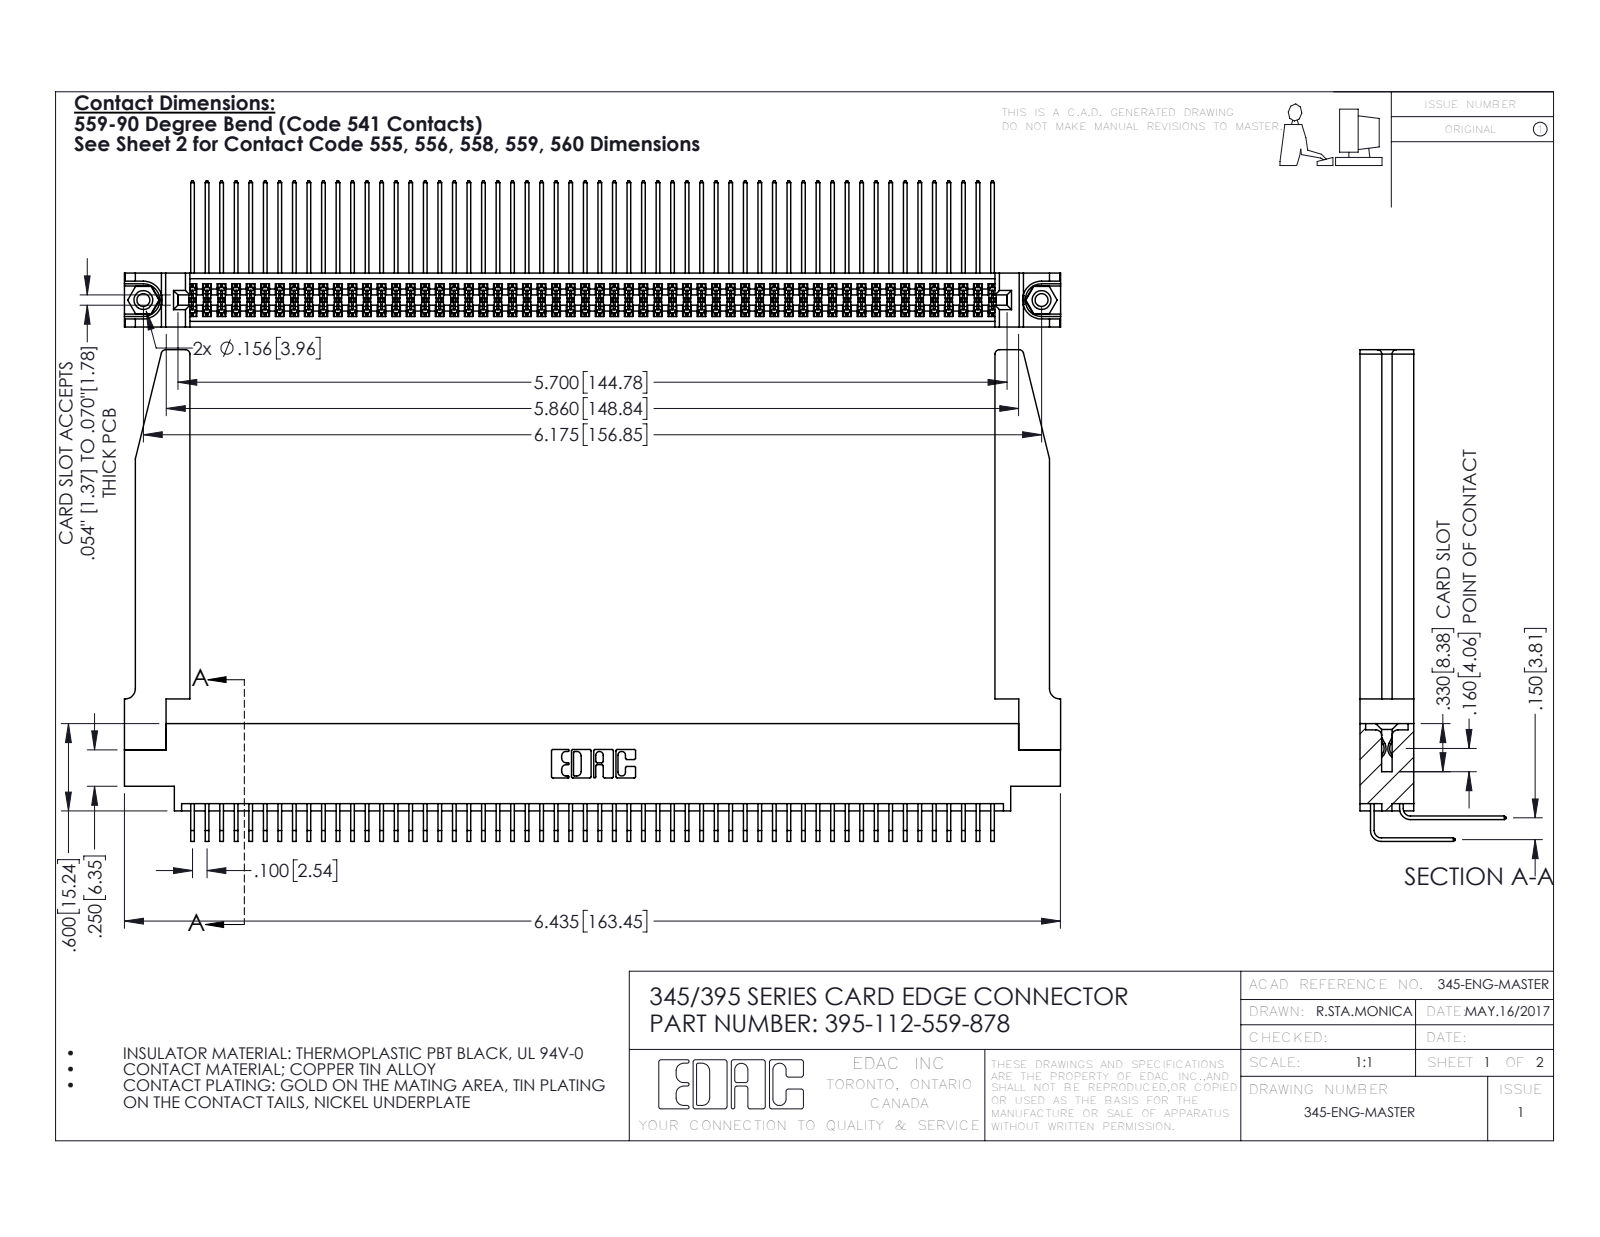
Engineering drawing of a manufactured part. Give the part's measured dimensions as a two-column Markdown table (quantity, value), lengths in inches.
| quantity | value |
| --- | --- |
| part name | 345 Part_0.170 Offset - 0.156 Dia-TH; 345-292-001_558 559 Tail - 1; 345-250-001_345-250-001-102; 345-292-001_559 Tail - 2 (+2 more) |
| STEP written by | SolidWorks 2016 (CONFIG_CONTROL_DESIGN) |
| units | inches |
| bodies | 117 solids, 6188 faces (4146 planar, 1990 cylindrical, 52 other) |
| overall size | 6.436 × 3.379 × 1.005 |
| volume | 1.484 in³ |
| surface area | 53.85 in² |
| round holes (diameter × count) | 0.089 × 2, 0.125 × 2, 0.156 × 2, 0.064 × 1 |
| round bosses / shafts (diameter × count) | 0.155 × 2 |
| partial cylindrical surfaces (radius × count) | 0.006 × 168, 0.01 × 22, 0.03 × 8, 0.007 × 6, 0.031 × 6, 0.026 × 3, 0.014 × 2, 0.019 × 2 |
| main face-to-face distances | 0.072, 0.37, 0.298, 0.098, 0.272, 0.025, 0.2, 0.225, 0.15, 0.175 |
| hole center spacings | 0.27, 5.939, 6.175 |
